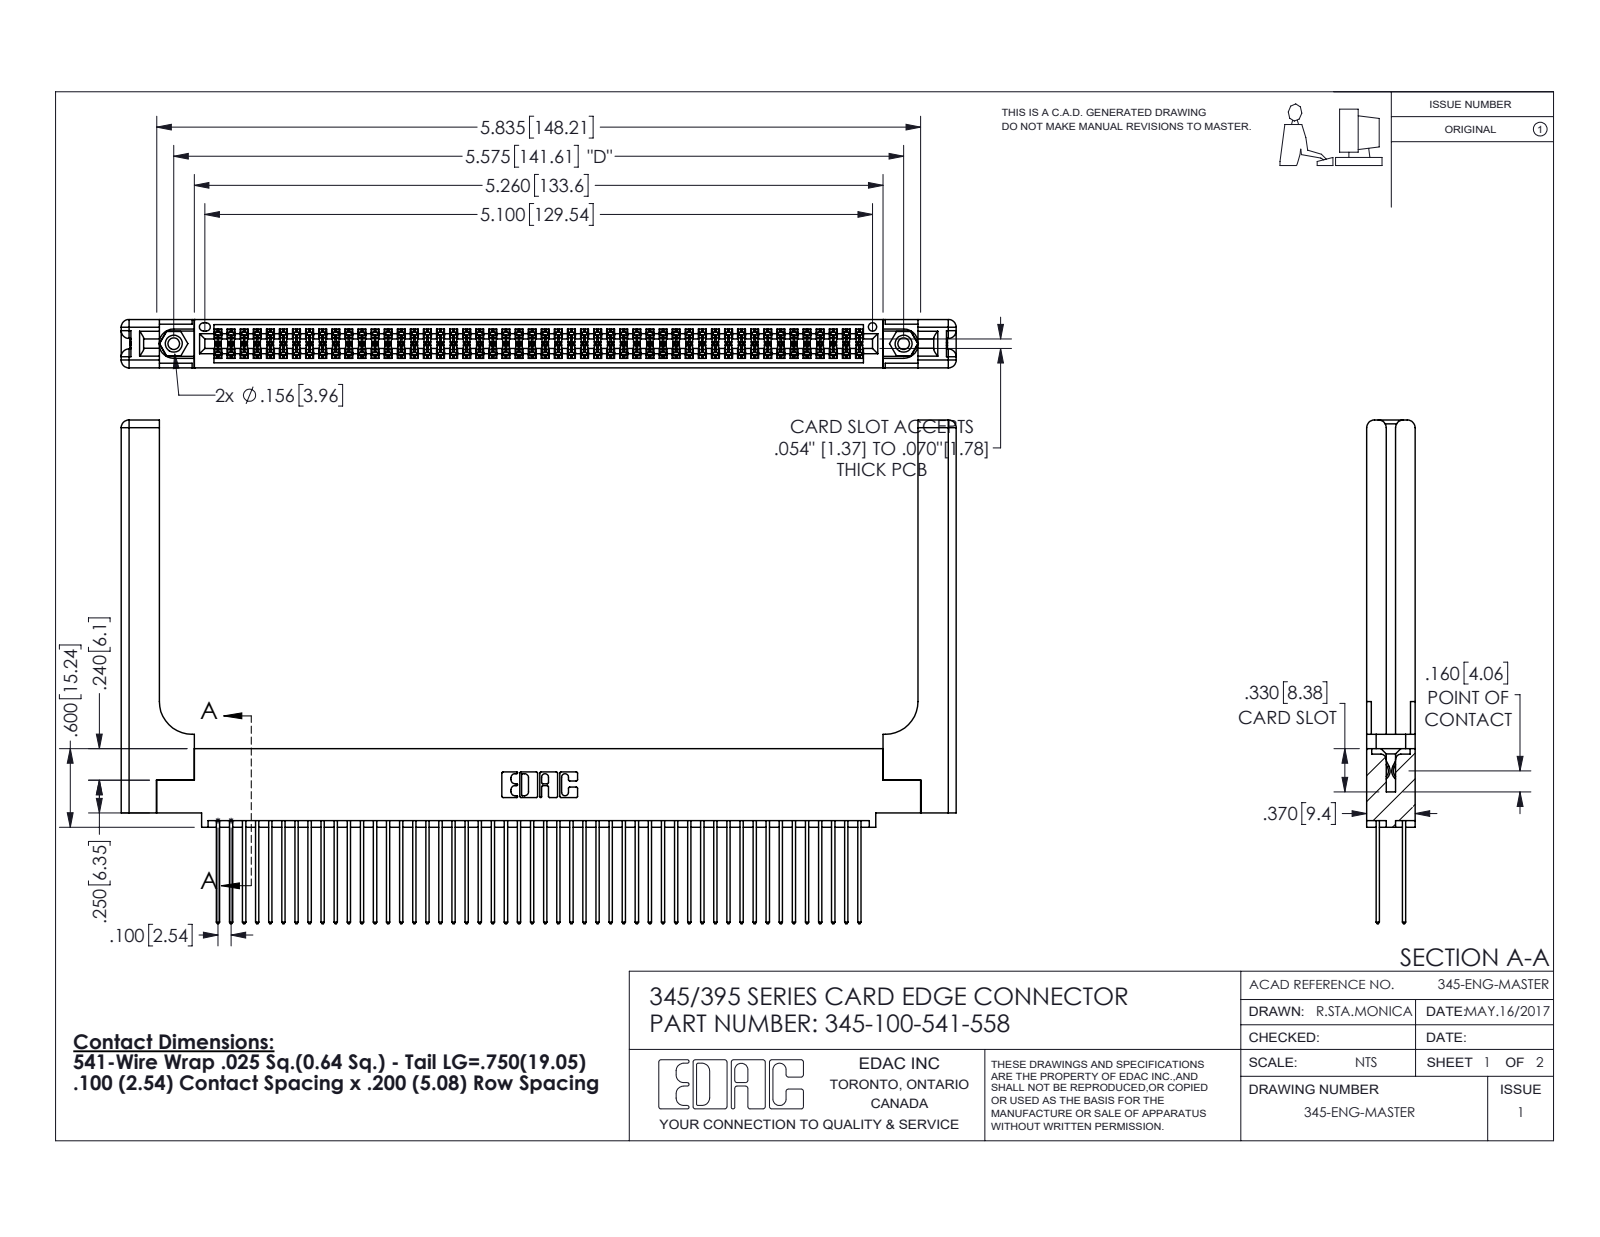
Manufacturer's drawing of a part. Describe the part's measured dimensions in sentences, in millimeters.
The part is named "345-292-001_345-293-141; 345-100-541-558; 345-220-058_345-220-058; 345-250-001_345-250-001-102 (+1 more)". Its 3-D file was written by "SolidWorks 2016 (CONFIG_CONTROL_DESIGN)". It is 105 solids with 5386 faces: 3532 planar, 1794 cylindrical and 60 other. Overall it measures 162 by 97.7 by 9.4 millimeters. Its volume is 24 790 cubic millimeters and its surface area 32 120 square millimeters. Round holes: 2 of diameter 2.3, 2 of diameter 3.2, 2 of diameter 4, 1 of diameter 1.6. Round bosses or shafts: 2 of diameter 3.9. Partial cylindrical surfaces (rounded edges, fillets, slot ends): 150 of radius 0.2, 100 of radius 0.3, 22 of radius 0.3, 16 of radius 1.5, 6 of radius 0.2, 6 of radius 0.8, 3 of radius 0.7, 2 of radius 0.4. The main face-to-face distances are 1.8, 7.6, 9.4, 2.5, 6.9, 0.6, 5.1, 5.7, 4.4, 3.8. The hole center spacings are 6.9, 135.6, 141.6.
